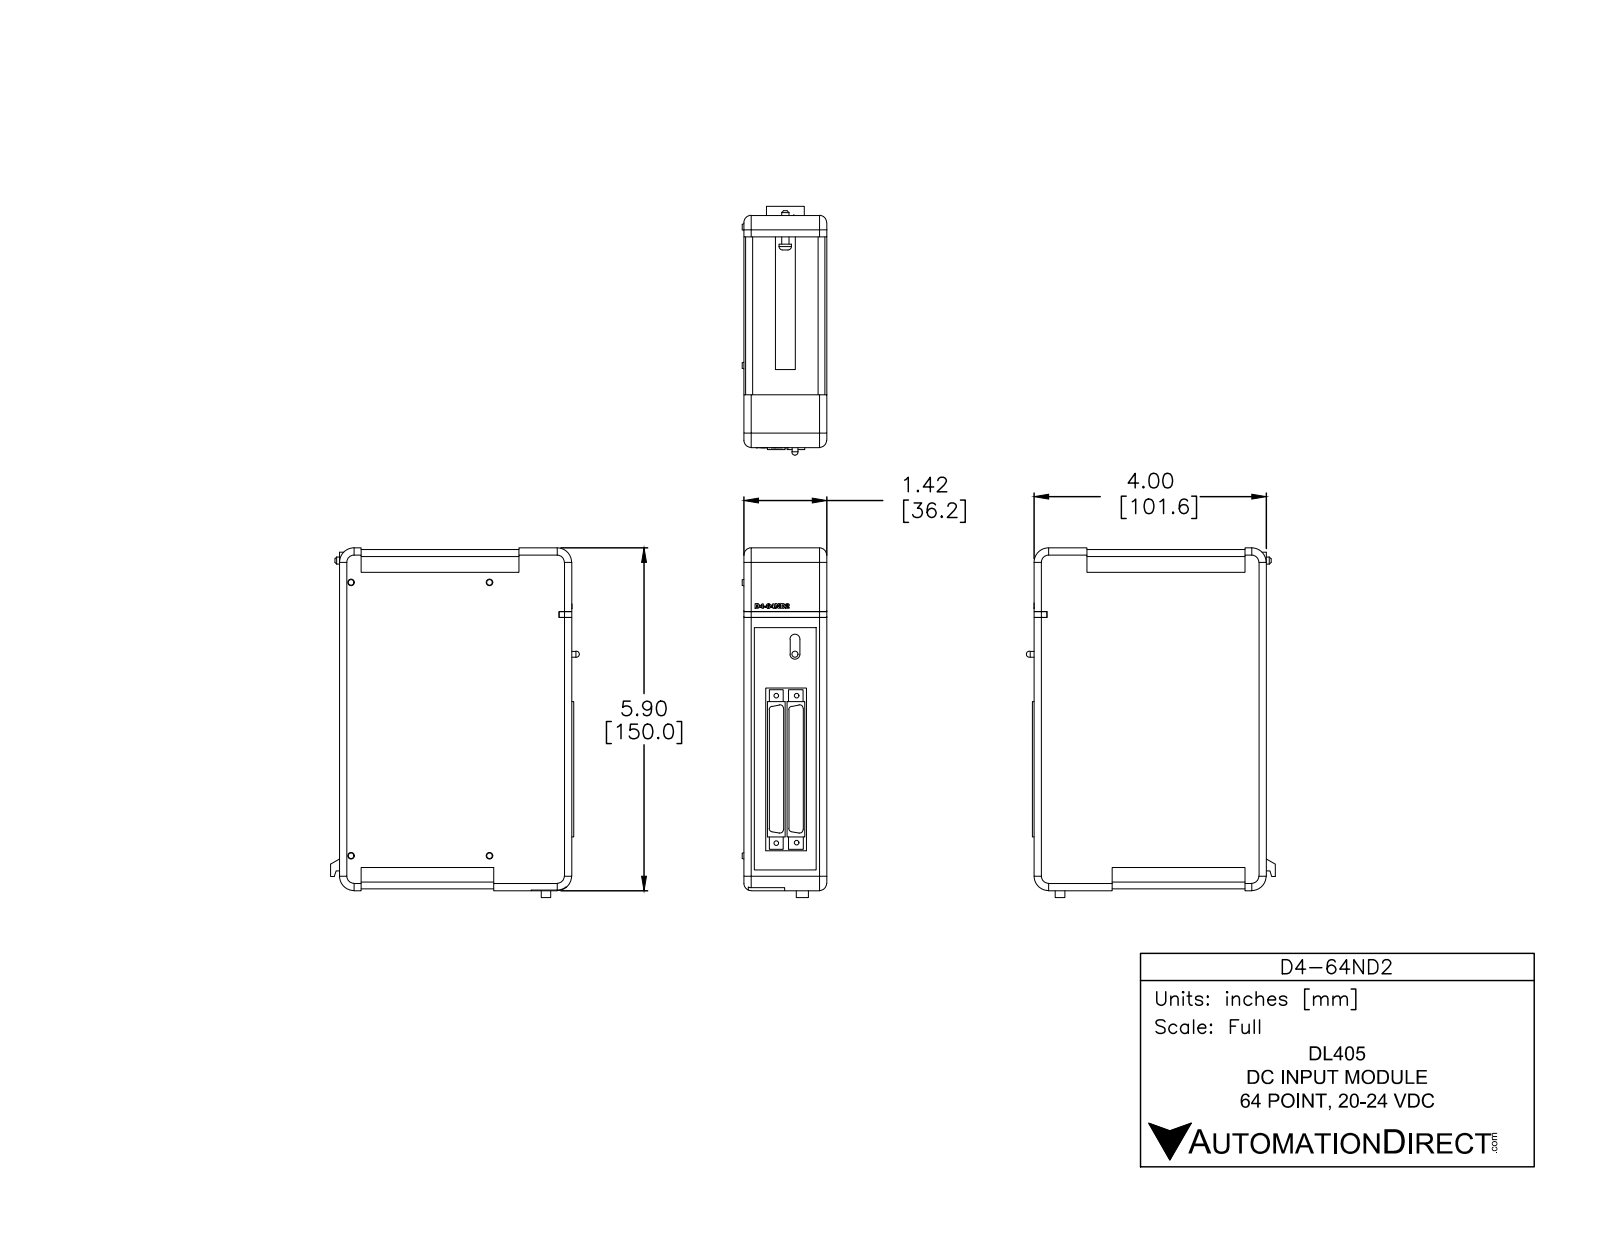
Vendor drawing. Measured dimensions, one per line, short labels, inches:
name: D4-64ND2
written by: SolidWorks 2014 (AUTOMOTIVE_DESIGN)
unit: in
bodies: 2 solids, 329 faces (213 planar, 54 cylindrical, 62 other)
size: 6.025 × 4.285 × 1.455
volume: 31.99 in³; area: 85.72 in²
holes: 4× ⌀0.08
bosses: 1× ⌀0.212, 1× ⌀0.123, 1× ⌀0.1
rounds: 8× R0.06, 8× R0.125, 4× R0.12, 4× R0.25, 2× R0.085, 1× R0.145, 1× R0.171
face distances: 1.425, 0.03, 1.395, 3.97, 5.845, 5.875, 4, 0.2, 0.155, 3.77
hole spacings: 0.351, 2.531, 2.539, 2.555, 2.563
